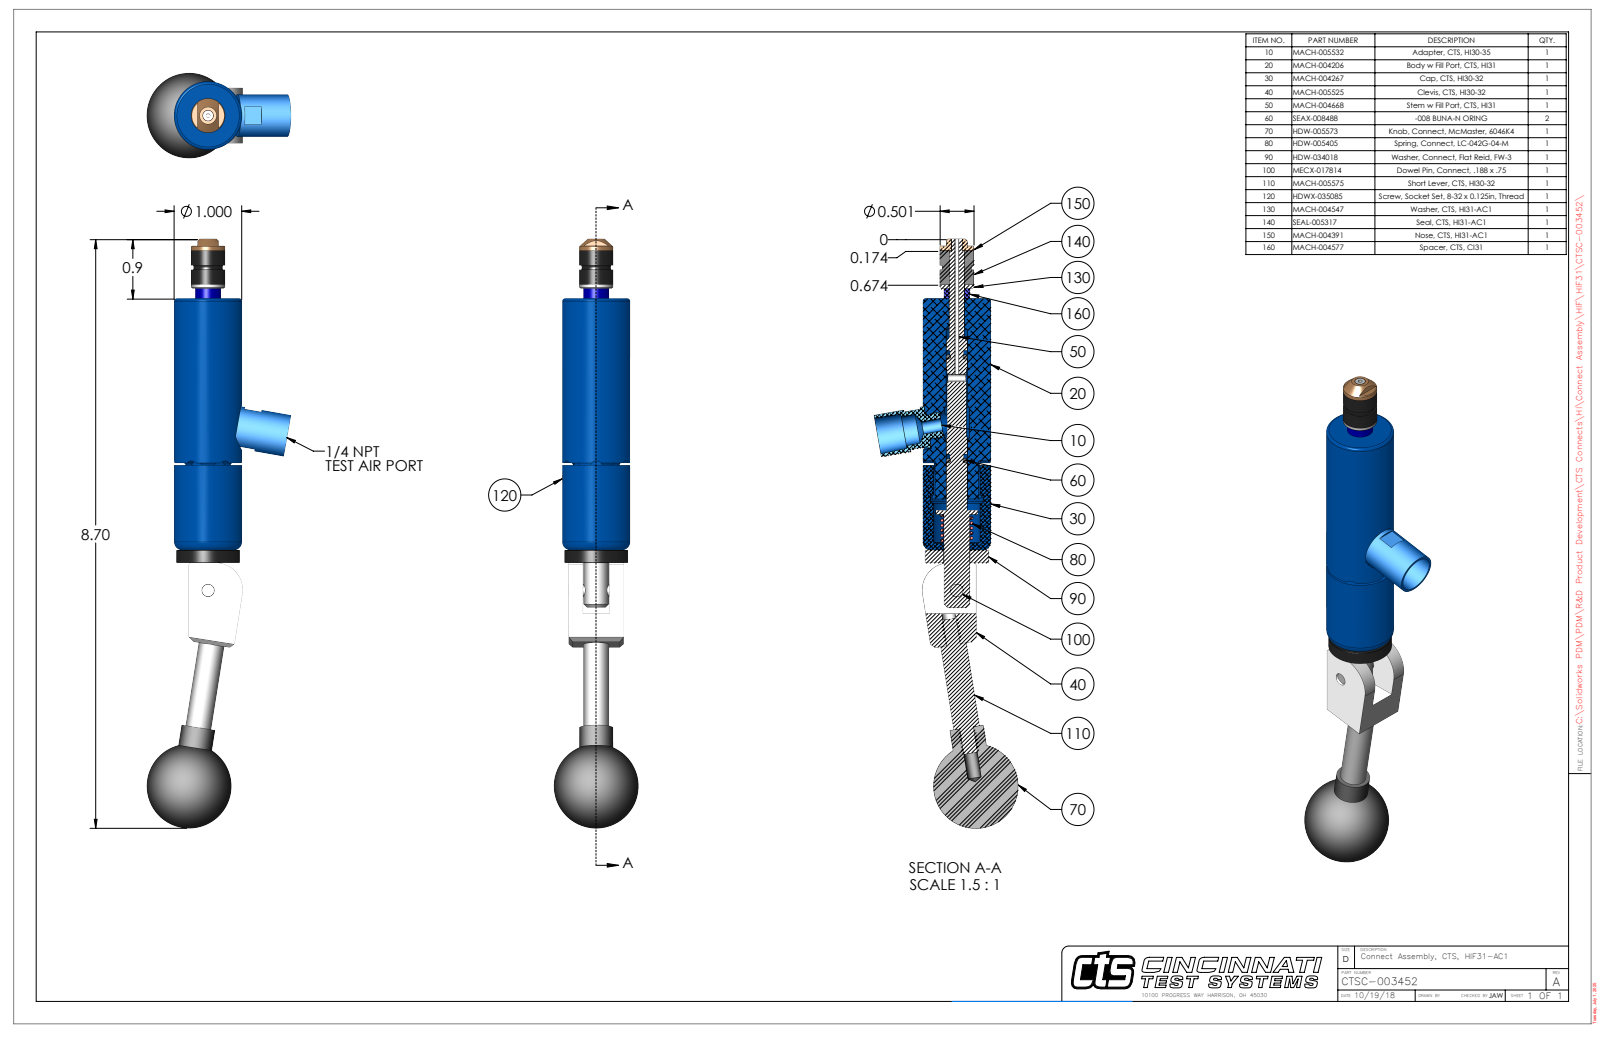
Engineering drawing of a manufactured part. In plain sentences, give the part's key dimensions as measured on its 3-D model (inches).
The part is named "CTSC-003452". Its 3-D file was written by "SolidWorks 2023 (AUTOMOTIVE_DESIGN)". It is 10 solids with 283 faces: 98 planar, 121 cylindrical and 64 other. Overall it measures 8.704 by 2.128 by 1.25 inches. Its volume is 5.01 cubic inches and its surface area 38.51 square inches. Round holes: 2 of diameter 0.201, 1 of diameter 0.063, 1 of diameter 0.109, 1 of diameter 0.136, 1 of diameter 0.15, 1 of diameter 0.159, 1 of diameter 0.187, 1 of diameter 0.189, 1 of diameter 0.218, 1 of diameter 0.228, 1 of diameter 0.229, 1 of diameter 0.385. Round bosses or shafts: 1 of diameter 1, 1 of diameter 0.936, 1 of diameter 0.62, 1 of diameter 0.501, 1 of diameter 0.5, 1 of diameter 0.38, 1 of diameter 0.379, 1 of diameter 0.375. Partial cylindrical surfaces (rounded edges, fillets, slot ends): 6 of radius 0.093, 2 of radius 0.029, 1 of radius 0.066, 1 of radius 0.325, 1 of radius 0.4, 1 of radius 0.473. The main face-to-face distances are 0.21, 0.602, 0.812, 0.187, 3.716, 3.903, 0.391, 2.463, 1.253, 1.441. The hole center spacings are 0.599, 1.658, 2.252.
